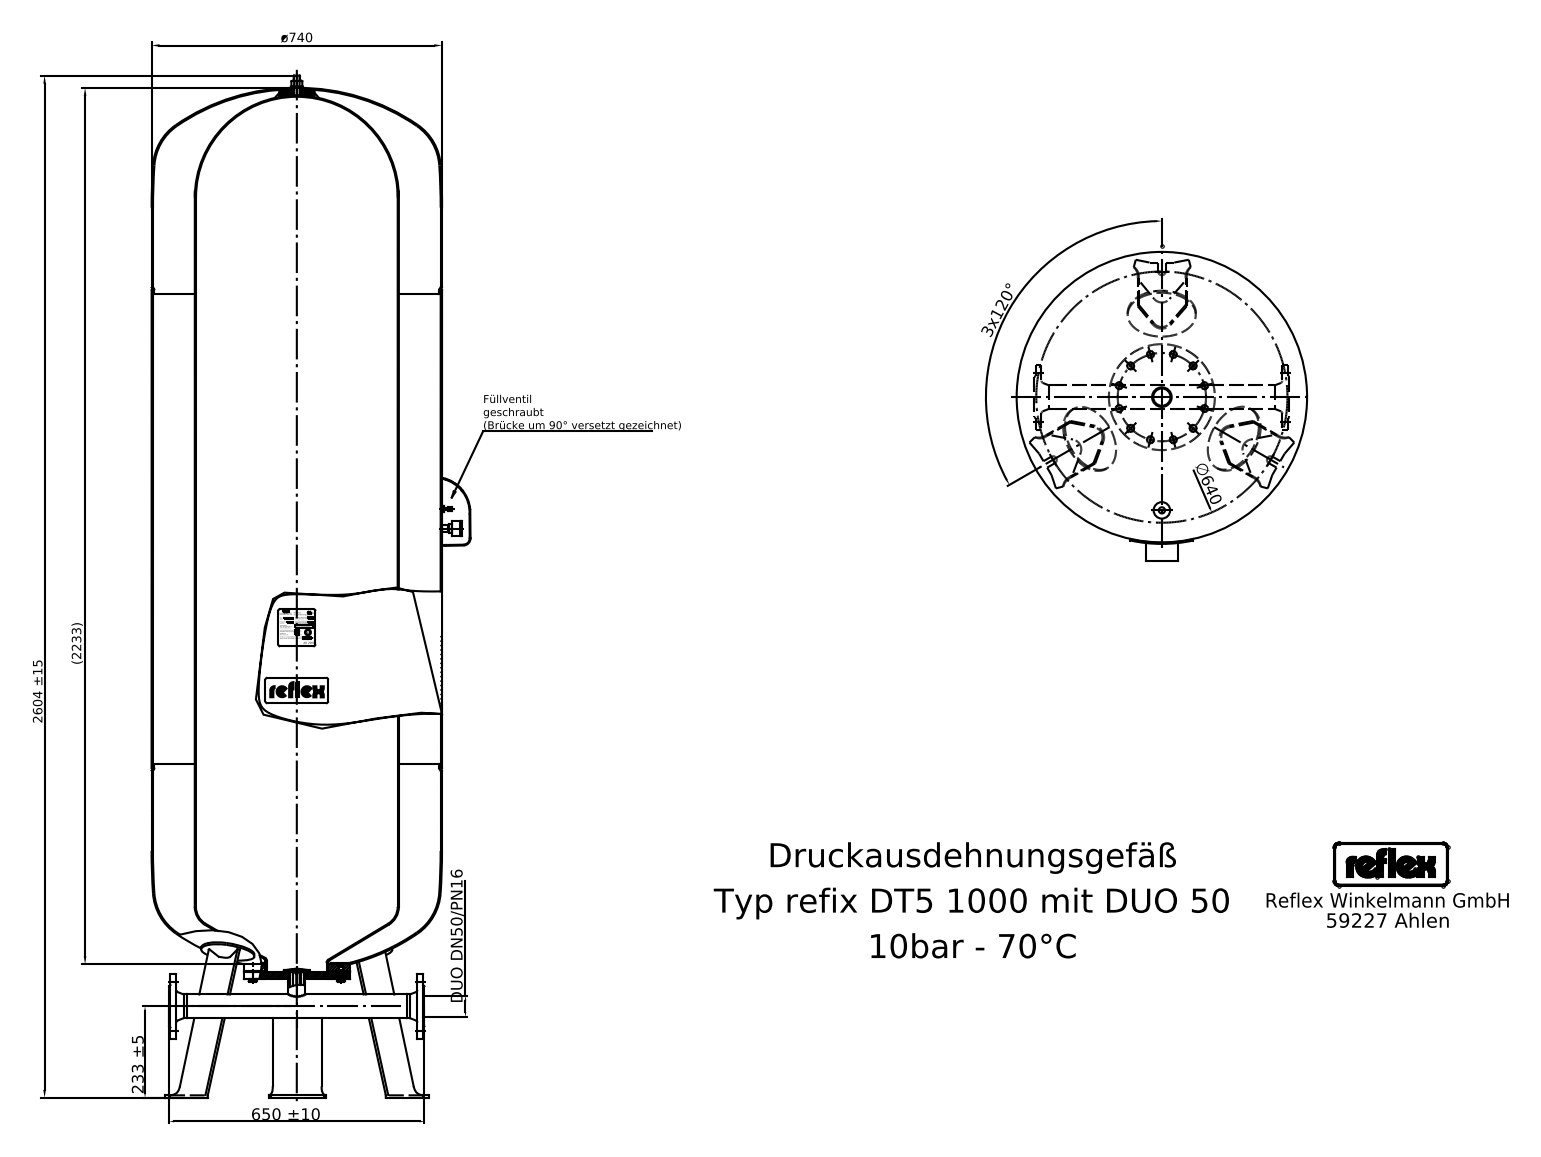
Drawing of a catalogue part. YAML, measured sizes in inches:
step_written_by: "Mechanical Desktop 2008 (CONFIG_CONTROL_DESIGN)"
units: inches
bodies: {solids: 26, faces: 522, planar: 233, cylindrical: 155, other: 134}
overall_size: [102.52, 31.894, 29.134]
volume: 55970
surface_area: 13100
round_holes:
  - {diameter: 0.748, count: 4}
  - {diameter: 0.098, count: 1}
  - {diameter: 0.15, count: 1}
  - {diameter: 0.169, count: 1}
  - {diameter: 0.173, count: 1}
  - {diameter: 0.215, count: 1}
  - {diameter: 0.276, count: 1}
  - {diameter: 0.315, count: 1}
  - {diameter: 0.449, count: 1}
  - {diameter: 2.374, count: 1}
  - {diameter: 6.181, count: 1}
  - {diameter: 9.843, count: 1}
round_bosses_or_shafts:
  - {diameter: 0.394, count: 9}
  - {diameter: 29.134, count: 1}
  - {diameter: 10.236, count: 1}
  - {diameter: 9.055, count: 1}
  - {diameter: 6.496, count: 1}
  - {diameter: 2.441, count: 1}
  - {diameter: 1.669, count: 1}
  - {diameter: 1.339, count: 1}
partial_cylinders:
  - {radius: 0.984, count: 18}
  - {radius: 0.221, count: 4}
  - {radius: 0.089, count: 3}
  - {radius: 0.354, count: 3}
  - {radius: 0.151, count: 2}
  - {radius: 0.266, count: 2}
  - {radius: 0.315, count: 2}
  - {radius: 0.365, count: 2}
face_to_face_distances: [73.701, 0.236, 7.677, 81.378, 0.235, 0.232, 7.913, 81.614, 12.244, 0.197]
hole_center_spacings: [2.46, 3.48, 4.921, 1.969]
